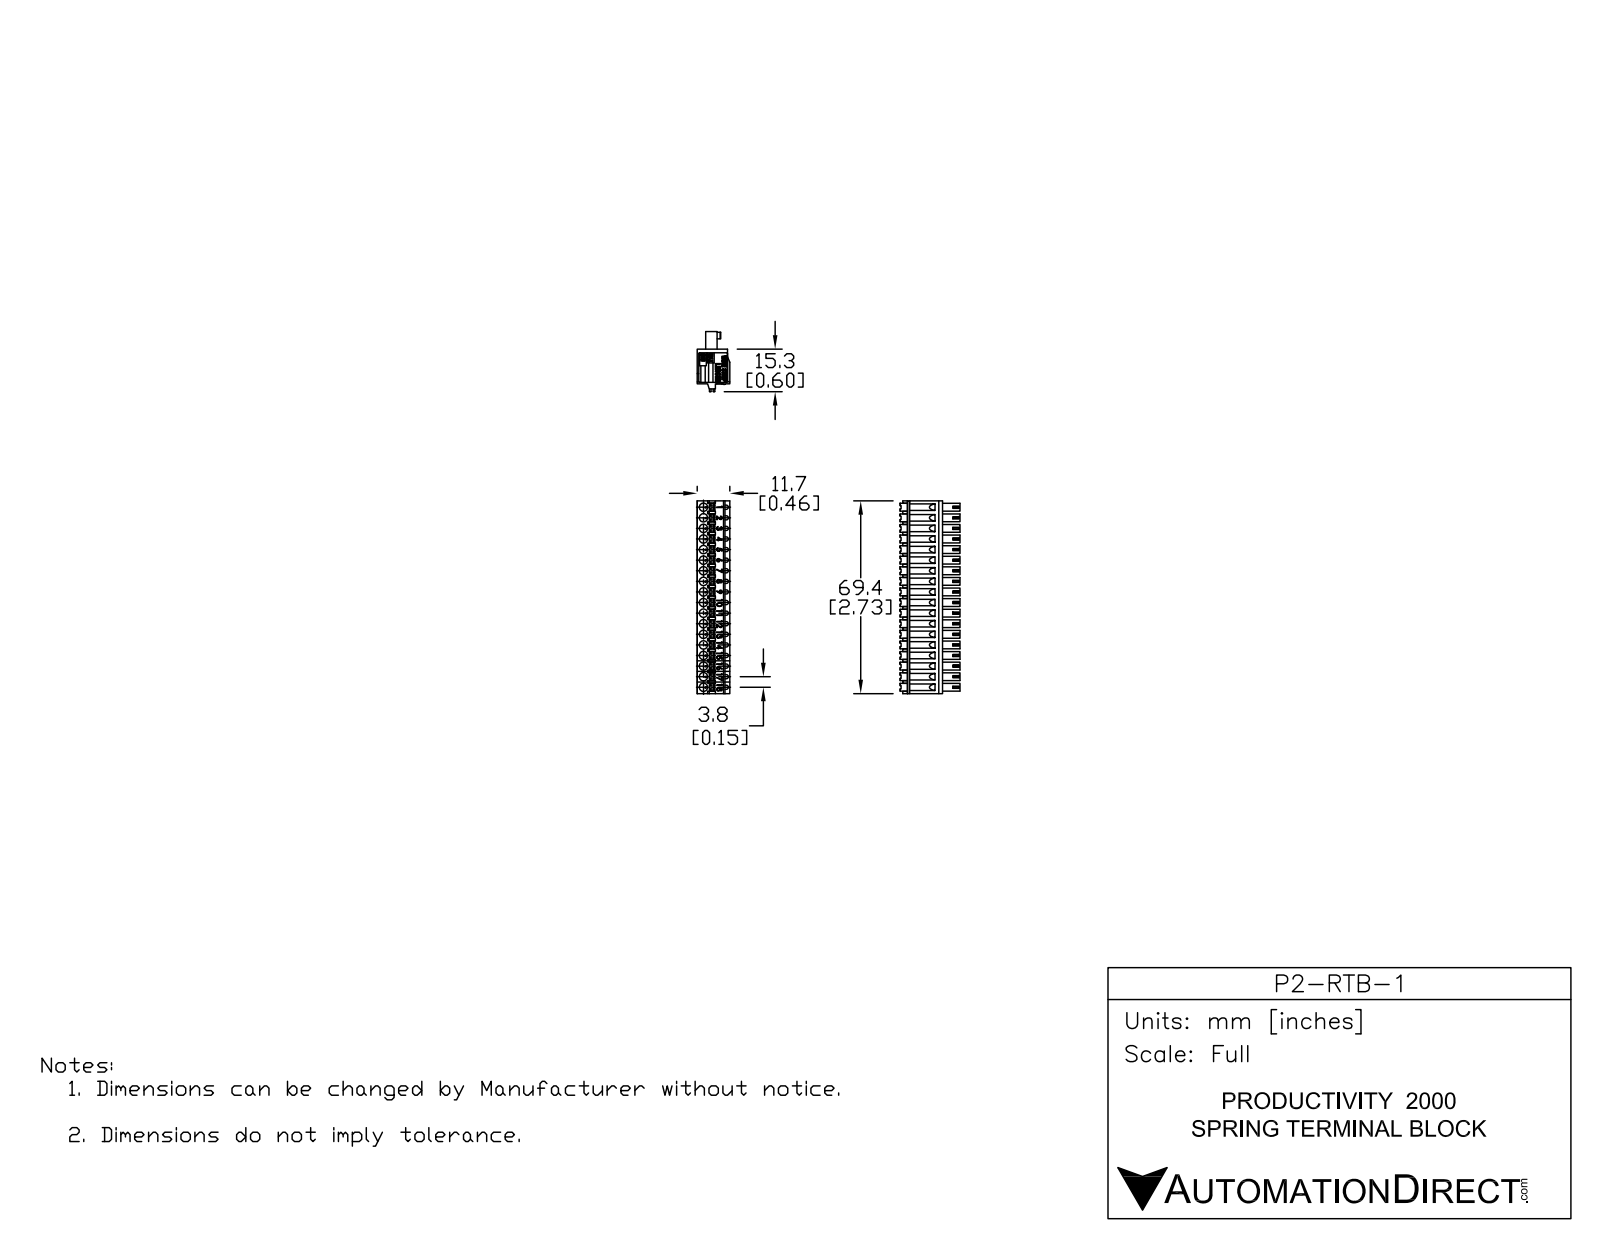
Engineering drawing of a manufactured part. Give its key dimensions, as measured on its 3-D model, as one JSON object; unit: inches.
{"part_name": "P2-RTB-1", "step_written_by": "SolidWorks 2017 (AUTOMOTIVE_DESIGN)", "units": "inches", "bodies": {"solids": 1, "faces": 1497, "planar": 1082, "cylindrical": 289, "other": 126}, "overall_size": [2.731, 0.858, 0.462], "volume_in3": 0.607, "surface_area_in2": 14.63, "round_holes": [[0.083, 18], [0.118, 18]], "partial_cylinders_radius": [[0.08, 19], [0.03, 18], [0.041, 18], [0.049, 18], [0.004, 4]], "face_to_face_distances": [0.492, 0.428, 0.15, 0.282, 0.146, 0.3, 0.45, 0.6, 0.035, 0.076], "hole_center_spacings": [0.15, 0.187, 0.3, 0.32, 0.45, 0.464, 0.6, 0.611]}
